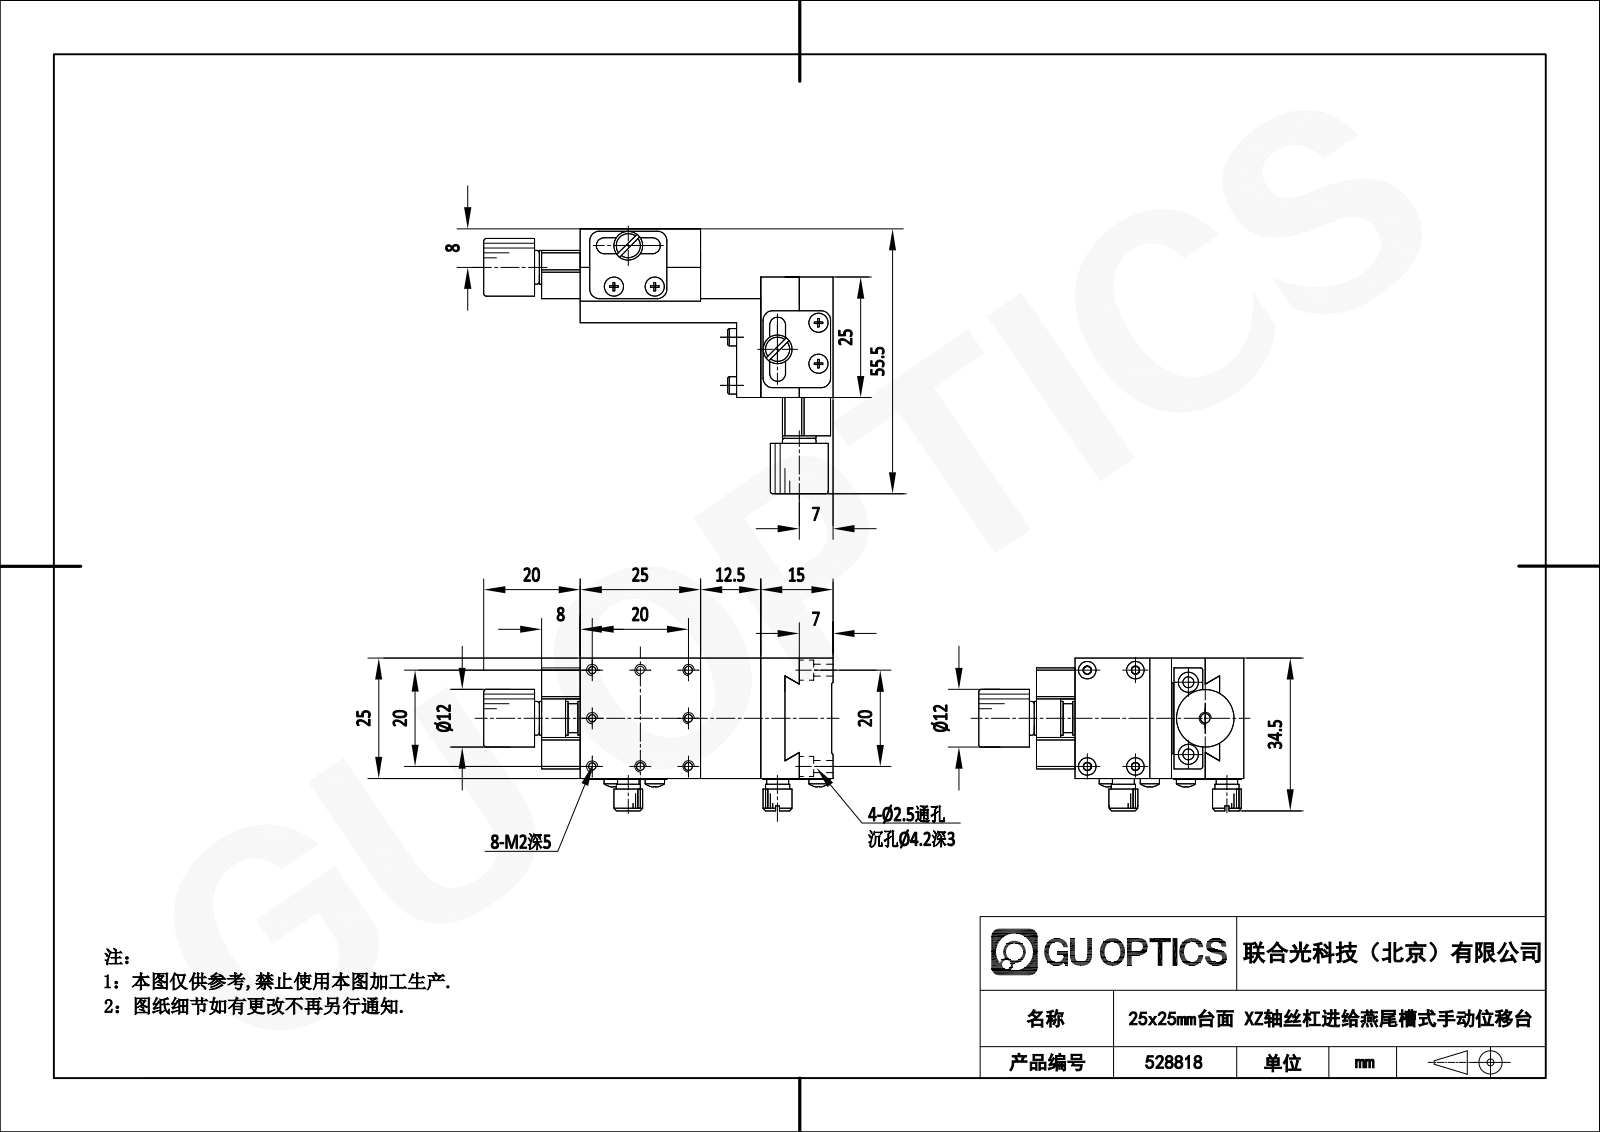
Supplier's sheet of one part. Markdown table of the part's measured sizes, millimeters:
| quantity | value |
| --- | --- |
| part name | 528818 |
| STEP written by | SolidWorks 2020 (CONFIG_CONTROL_DESIGN) |
| units | millimeters |
| bodies | 7 solids, 1212 faces (516 planar, 292 cylindrical, 404 other) |
| overall size | 72.5 × 55.5 × 34.5 |
| volume | 26 911 mm³ |
| surface area | 20 672 mm² |
| round holes (diameter × count) | 1.57 × 24, 2.5 × 20, 4 × 10, 4.2 × 8, 1.57 × 7, 2.2 × 4, 2.46 × 4, 2.01 × 3, 2.01 × 3, 2.46 × 2, 7 × 2 |
| round bosses / shafts (diameter × count) | 6 × 2, 4 × 2, 3 × 2, 2 × 2 |
| partial cylindrical surfaces (radius × count) | 1 × 16, 1.25 × 4, 3 × 2, 6 × 2 |
| main face-to-face distances | 8, 4, 15, 5, 20, 0.5, 10, 25, 7, 7.5 |
| hole center spacings | 10, 22.36, 20, 10.44, 12.21, 14.14, 16.4, 7 |
